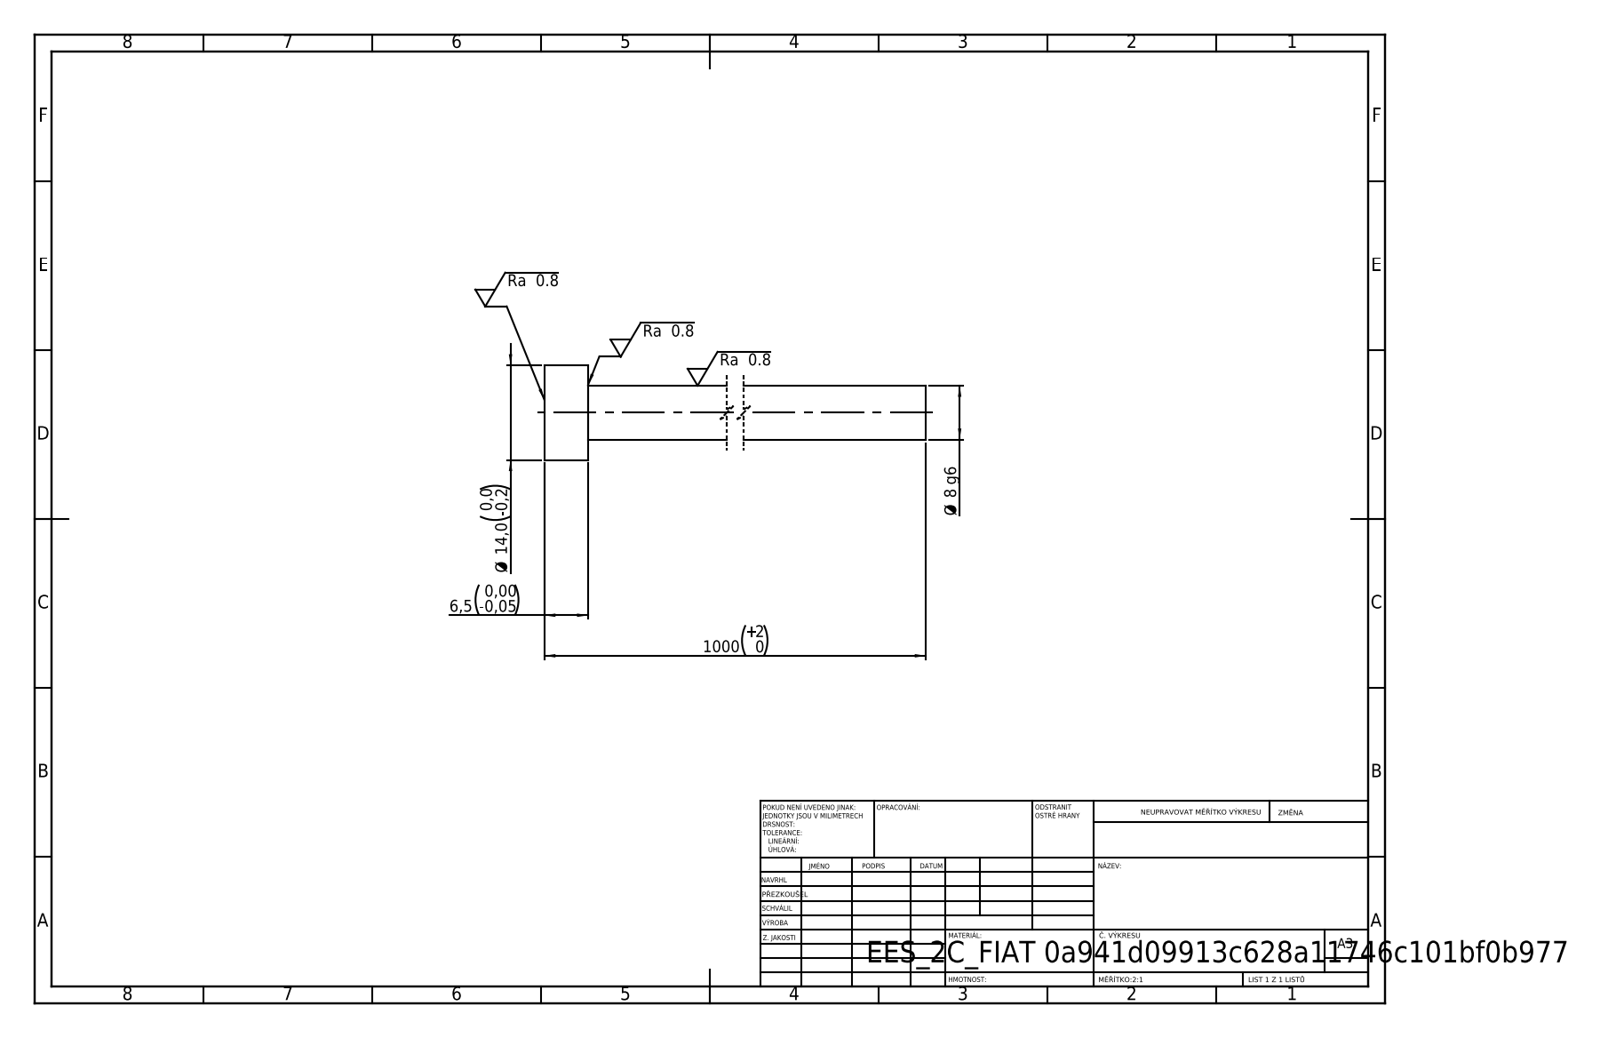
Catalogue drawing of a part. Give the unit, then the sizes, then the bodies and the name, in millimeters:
Units: millimetres
Overall size (bounding box): 1000 × 14 × 14
Round bosses / shafts (diameter × count): ⌀14 ×1, ⌀8 ×1
Main face-to-face distances: 6.5, 1000, 993.5
Volume: 50 939 mm³ · Surface area: 25 563 mm²
Bodies: 1 solid, 7 faces (3 planar, 4 cylindrical, 0 other)
STEP written by: SolidWorks 2019 (CONFIG_CONTROL_DESIGN)
